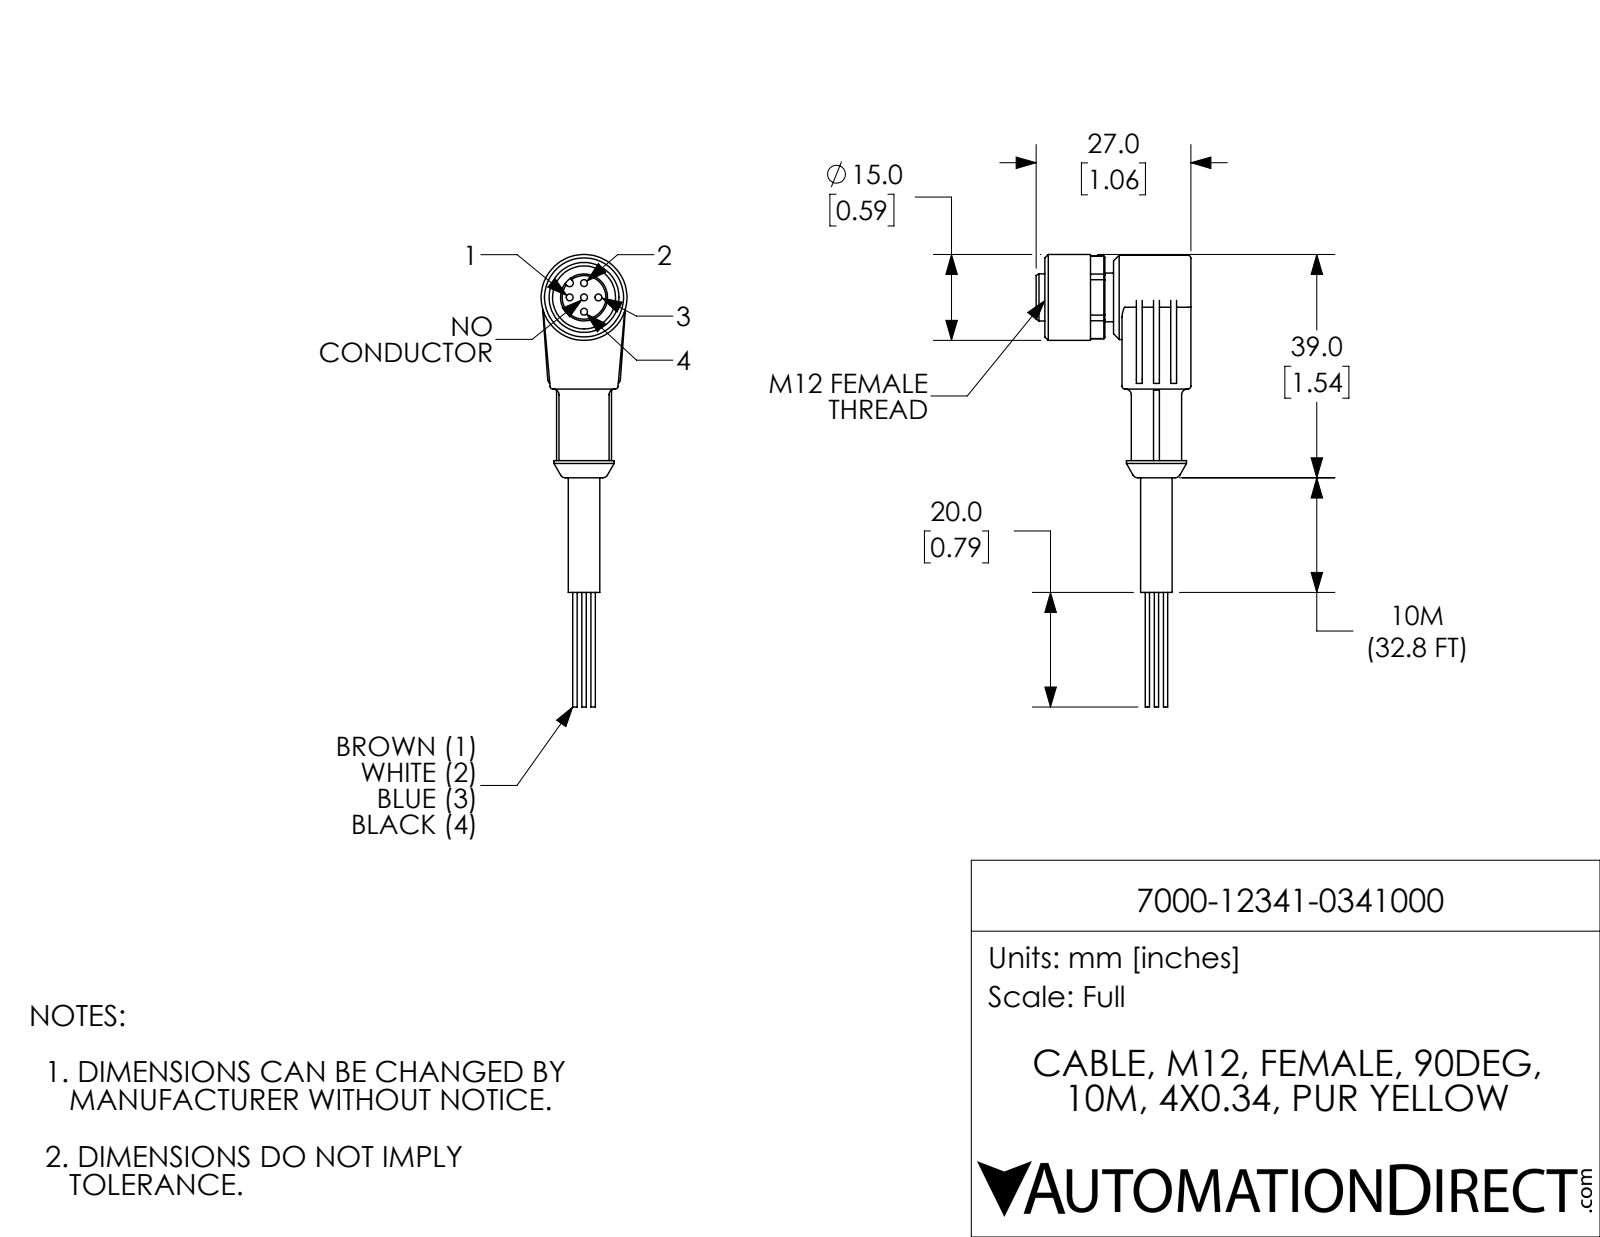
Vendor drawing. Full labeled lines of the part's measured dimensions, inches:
Part name (STEP PRODUCT): 7000-12341-0341000
STEP written by: SolidWorks 2021 (CONFIG_CONTROL_DESIGN)
Units: inches
Bodies: 1 solid, 152 faces (65 planar, 59 cylindrical, 28 other)
Overall size (bounding box): 3.11 × 1.063 × 0.591
Volume: 0.417 in³ · Surface area: 5.896 in²
Round holes (diameter × count): ⌀0.047 ×5, ⌀0.189 ×1, ⌀0.433 ×1
Round bosses / shafts (diameter × count): ⌀0.03 ×4, ⌀0.591 ×1, ⌀0.579 ×1, ⌀0.413 ×1, ⌀0.346 ×1, ⌀0.335 ×1, ⌀0.323 ×1, ⌀0.217 ×1
Partial cylindrical surfaces — rounded edges, fillets, slot ends (radius × count): R0.02 ×8, R0.039 ×2, R0.026 ×1, R0.283 ×1
Main face-to-face distances: 0.472, 0.059, 0.118, 0.531, 0.591, 0.217, 0.374, 0.236, 0.315, 0.492
Hole centre spacings: 0.098, 0.139, 0.197
